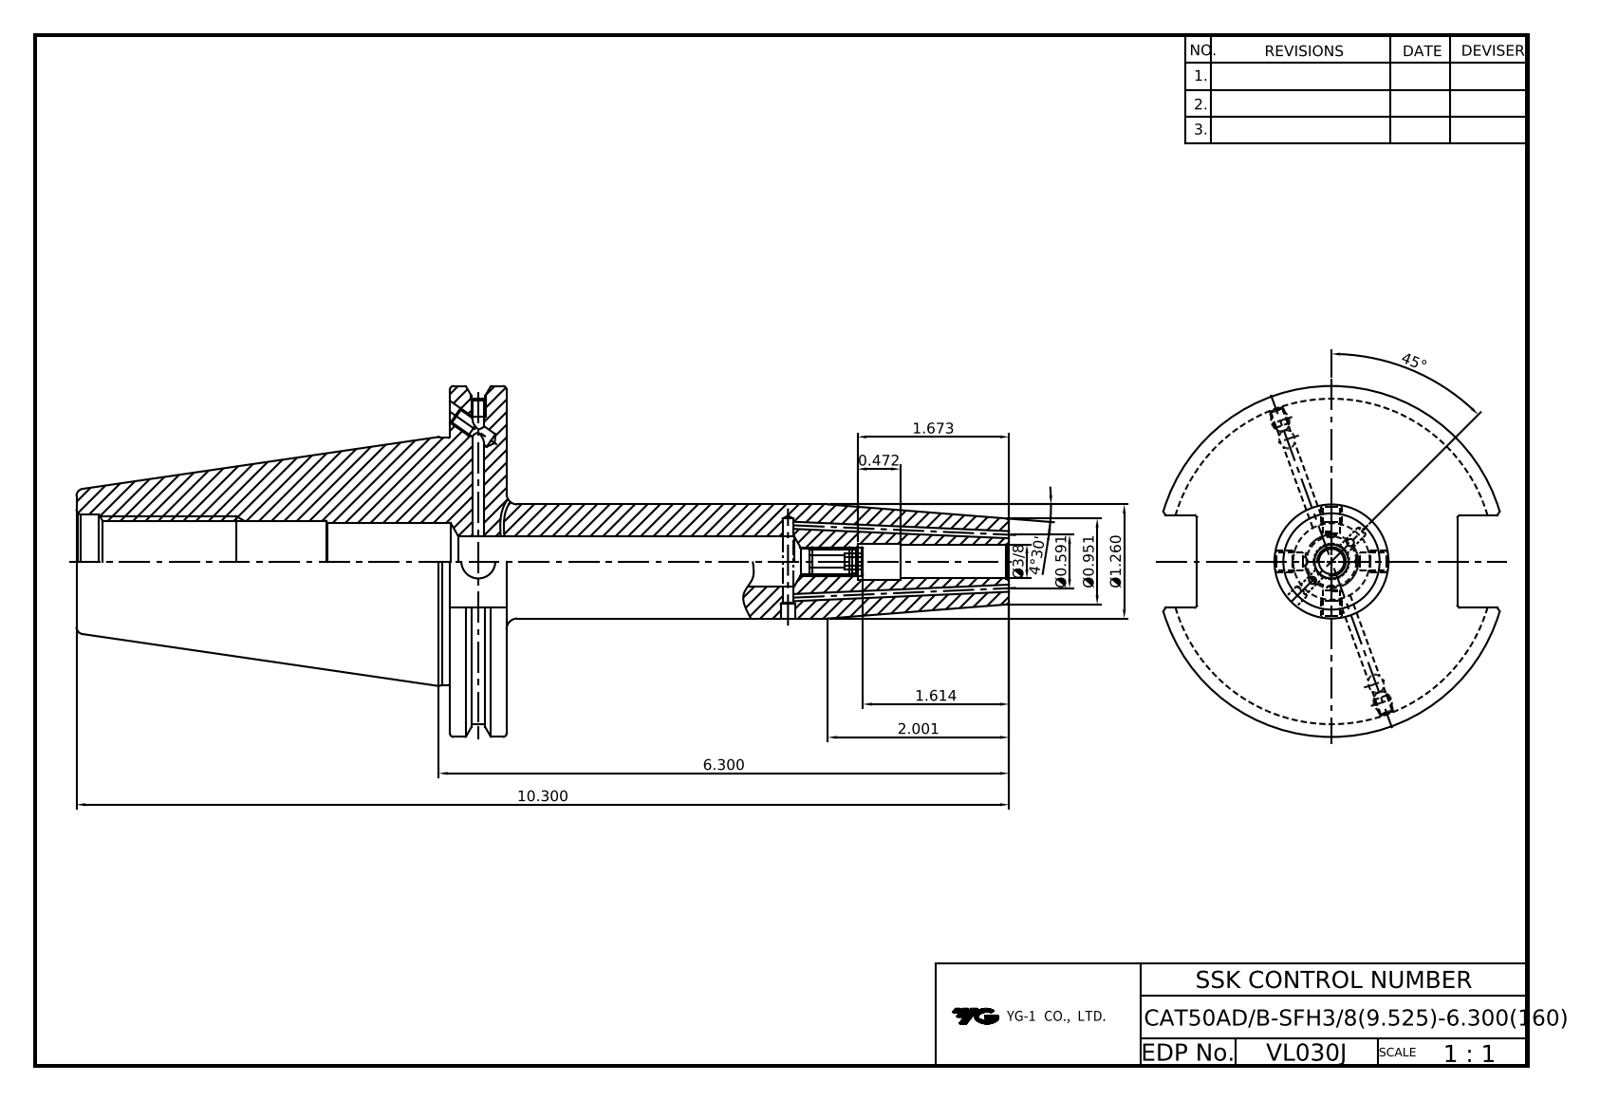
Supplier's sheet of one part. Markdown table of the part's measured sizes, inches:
| quantity | value |
| --- | --- |
| part name | LO-CAT50ADB-SFH9.525C-160 |
| STEP written by | Autodesk Inventor 2022 (AUTOMOTIVE_DESIGN) |
| units | inches |
| bodies | 1 solid, 92 faces (37 planar, 30 cylindrical, 25 other) |
| overall size | 10.299 × 3.875 × 3.728 |
| volume | 25.42 in³ |
| surface area | 96.89 in² |
| round holes (diameter × count) | 0.079 × 2, 0.128 × 2, 0.163 × 2, 0.165 × 2, 0.197 × 2, 0.375 × 2, 0.272 × 1, 0.394 × 1, 0.422 × 1, 0.846 × 1, 0.865 × 1, 1.031 × 1 |
| round bosses / shafts (diameter × count) | 3.875 × 1, 3.594 × 1, 2.726 × 1, 1.26 × 1 |
| main face-to-face distances | 0.625, 4.125, 4.75, 2.875, 1.02, 10.299, 6.174, 5.549, 4.363, 0.238 |
